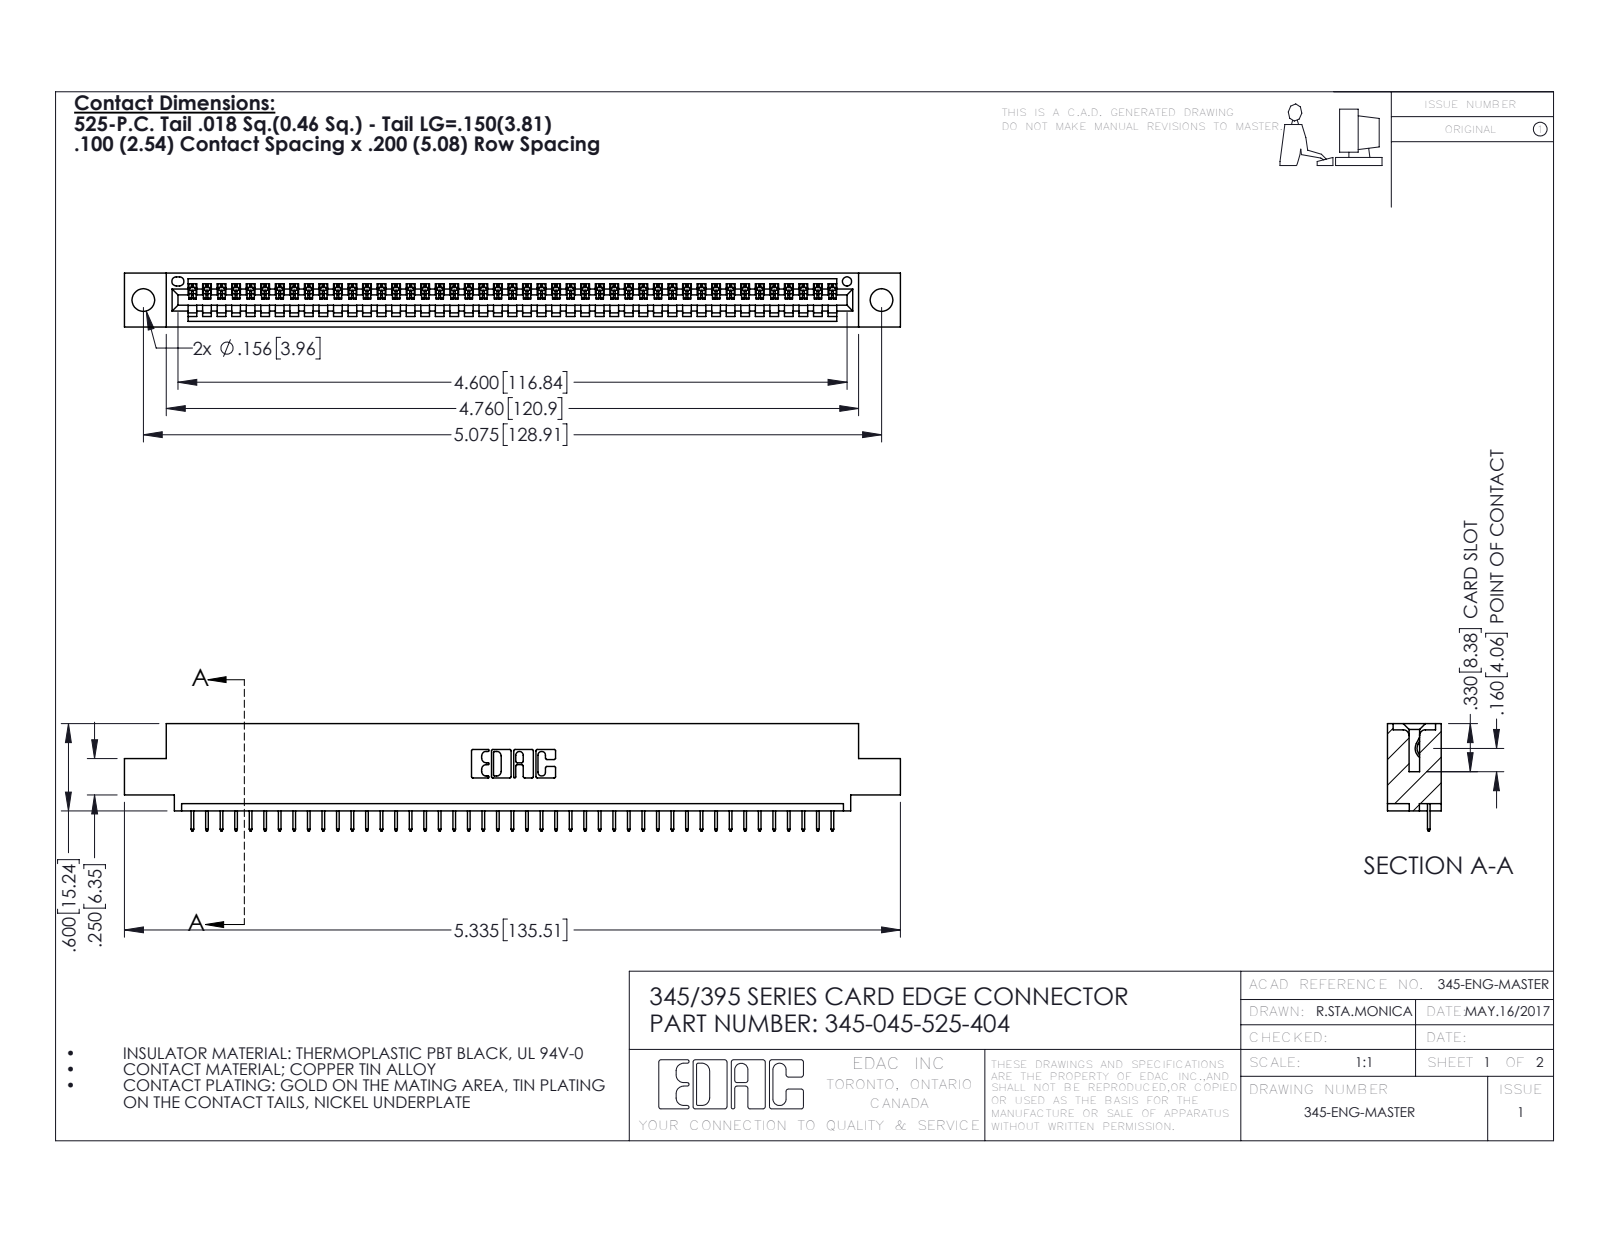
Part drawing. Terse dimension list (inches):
name: 345-045-525-404; 345-292-001_345-293-125; 345 Part_0.110 Offset - 0.156 Dia-TH
written by: SolidWorks 2020 (CONFIG_CONTROL_DESIGN)
unit: in
bodies: 46 solids, 2920 faces (2154 planar, 766 cylindrical, 0 other)
size: 5.335 × 0.737 × 0.37
volume: 0.766 in³; area: 24.8 in²
holes: 2× ⌀0.156, 1× ⌀0.064
rounds: 90× R0.006, 22× R0.01, 6× R0.007, 6× R0.031, 3× R0.026, 2× R0.031, 2× R0.04, 1× R0.014
face distances: 0.072, 0.298, 0.37, 0.2, 0.098, 0.272, 0.025, 0.225, 0.072, 0.149
hole spacings: 0.27, 4.839, 5.075
